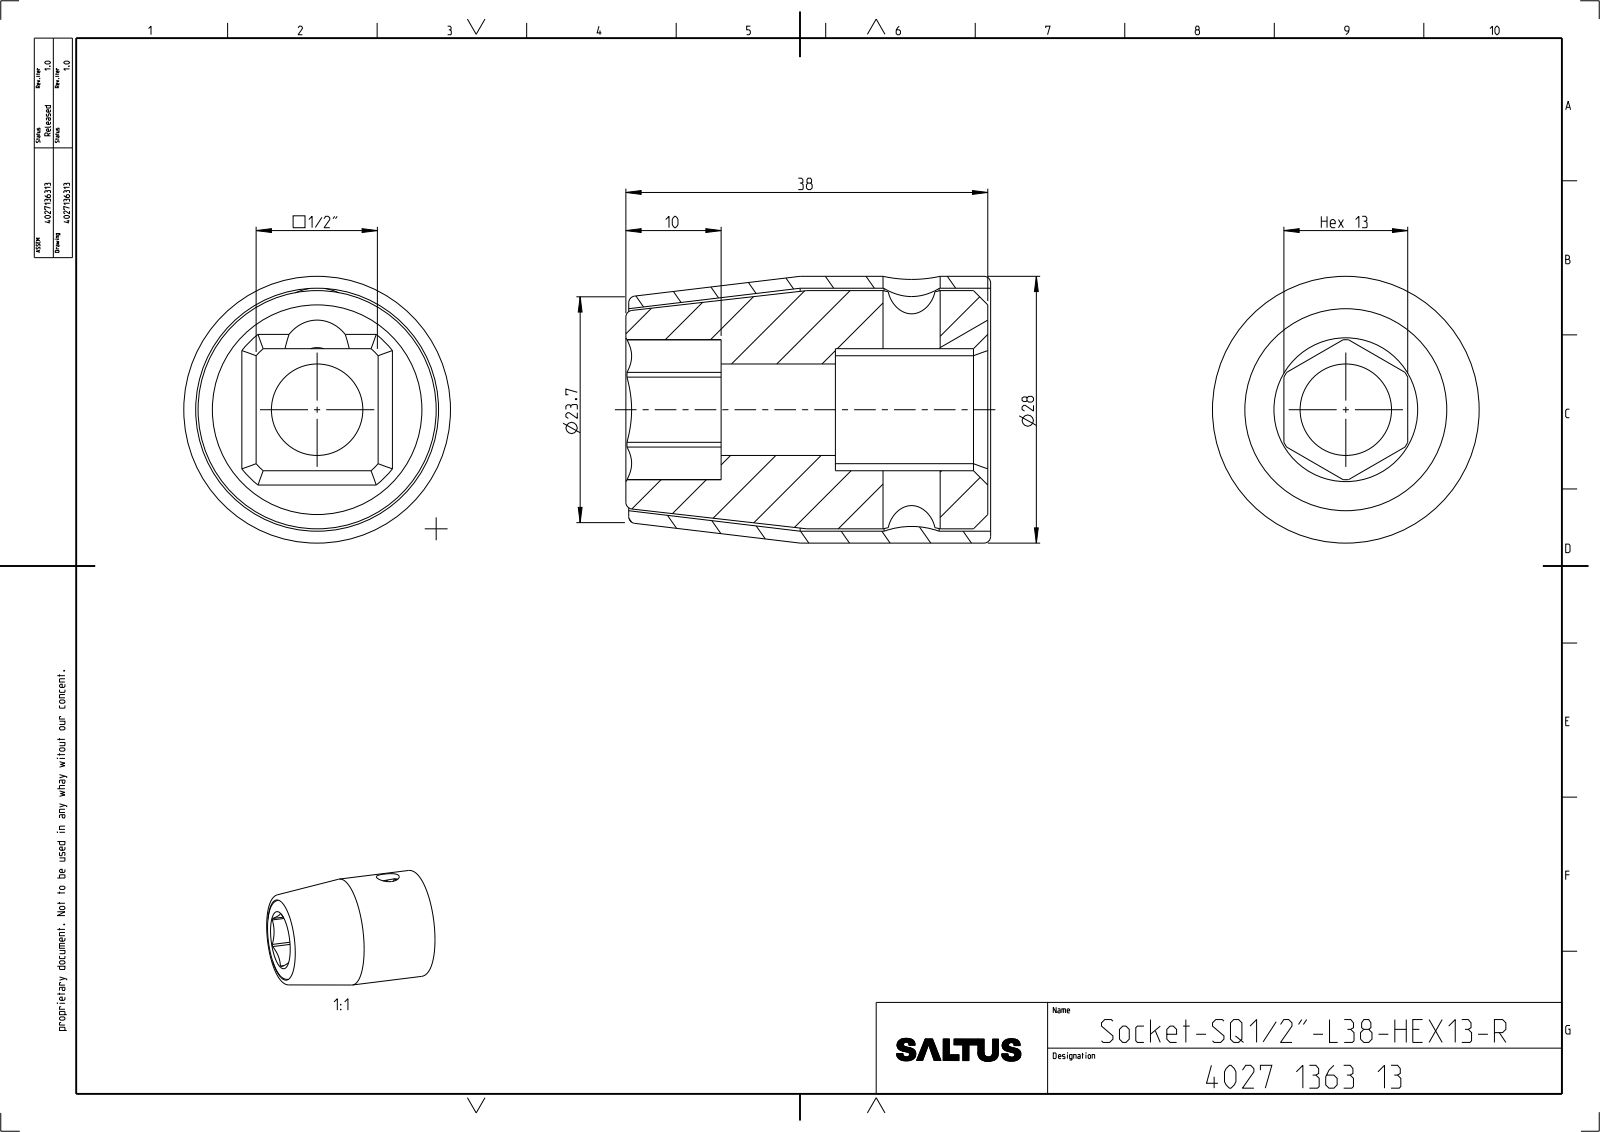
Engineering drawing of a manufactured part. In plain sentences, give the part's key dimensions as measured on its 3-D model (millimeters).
The part is named "4027130013; 4027039676; 4027136313_ASM". Its 3-D file was written by "CREO PARAMETRIC BY PTC INC, 2022414 (CONFIG_CONTROL_DESIGN)". It is 2 solids with 73 faces: 21 planar, 29 cylindrical and 23 other. Overall it measures 38.3 by 28 by 28 millimeters. Its volume is 15 154 cubic millimeters and its surface area 11 441 square millimeters. Round holes: 1 of diameter 6, 1 of diameter 9.6, 1 of diameter 25.5. Round bosses or shafts: 1 of diameter 28, 1 of diameter 25. Partial cylindrical surfaces (rounded edges, fillets, slot ends): 1 of radius 4, 1 of radius 7.34, 1 of radius 8.55. The main face-to-face distances are 12.82, 38, 12.99, 12.91, 16, 22, 28, 12, 10, 13.
